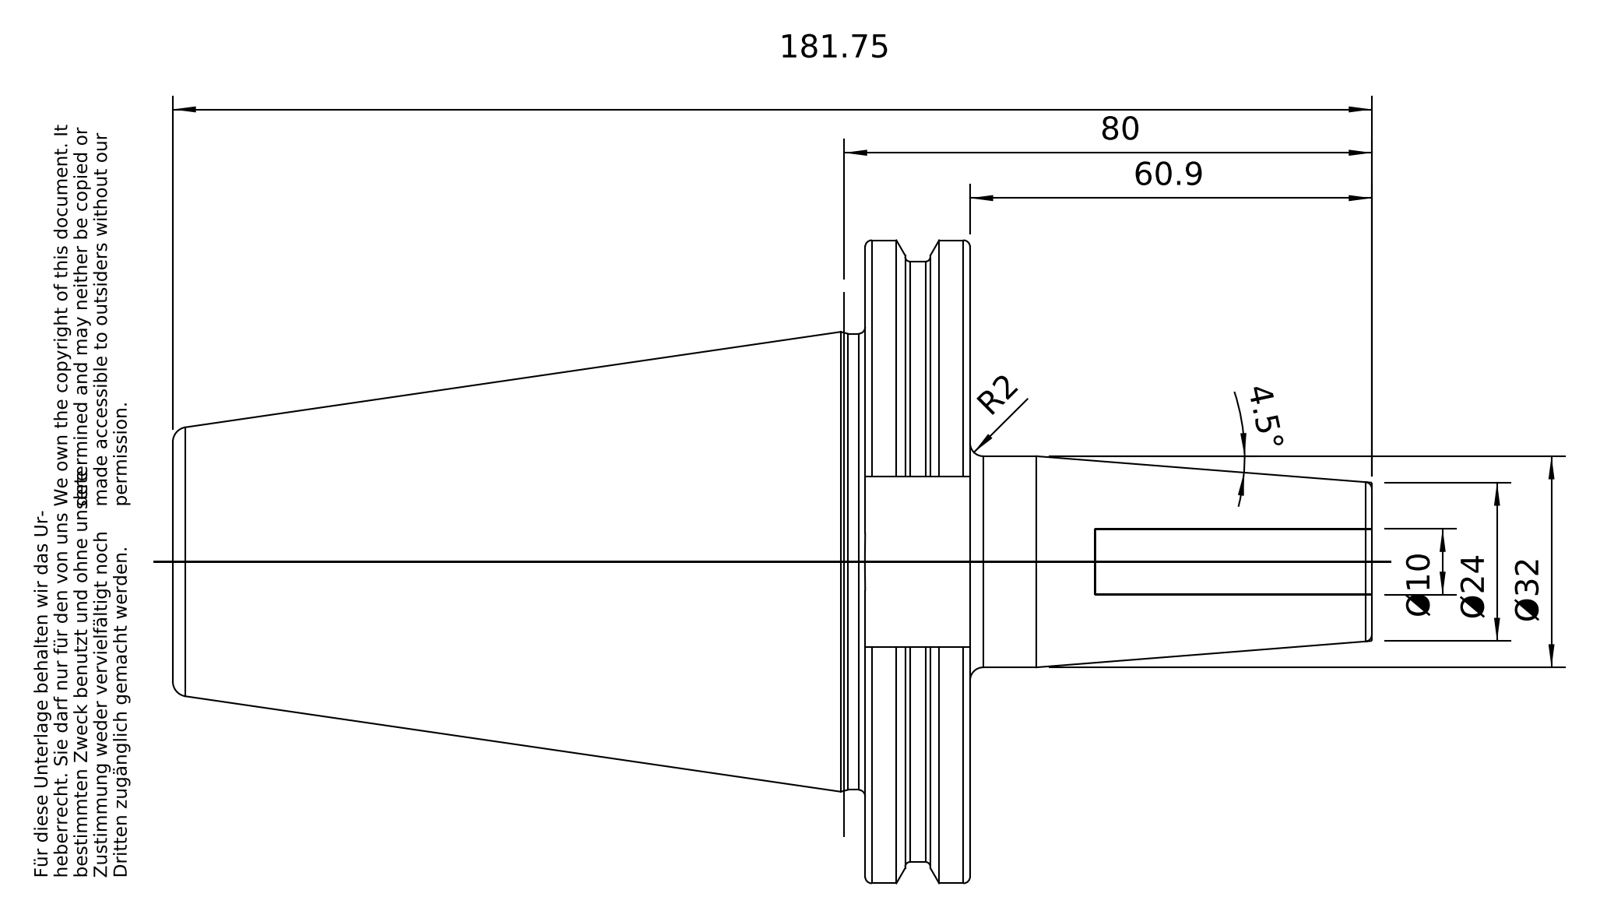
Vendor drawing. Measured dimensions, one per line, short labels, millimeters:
name: 50-440-10
written by: PRO/ENGINEER BY PARAMETRIC TECHNOLOGY CORPORATION, 2010430 (CONFIG_CONTROL_DESIGN)
unit: mm
bodies: 1 solid, 93 faces (21 planar, 24 cylindrical, 48 other)
size: 181.6 × 97.47 × 94
volume: 375 763 mm³; area: 49 001 mm²
holes: 1× ⌀10, 1× ⌀20.75, 1× ⌀25.01, 1× ⌀25.7
bosses: 1× ⌀91, 1× ⌀69.15, 1× ⌀32, 1× ⌀24.01
rounds: 1× R1.75, 1× R48.74
face distances: 15.85, 72.8, 104.8, 120.65, 181.6, 76.8, 60.95, 25.8, 48, 56.8
